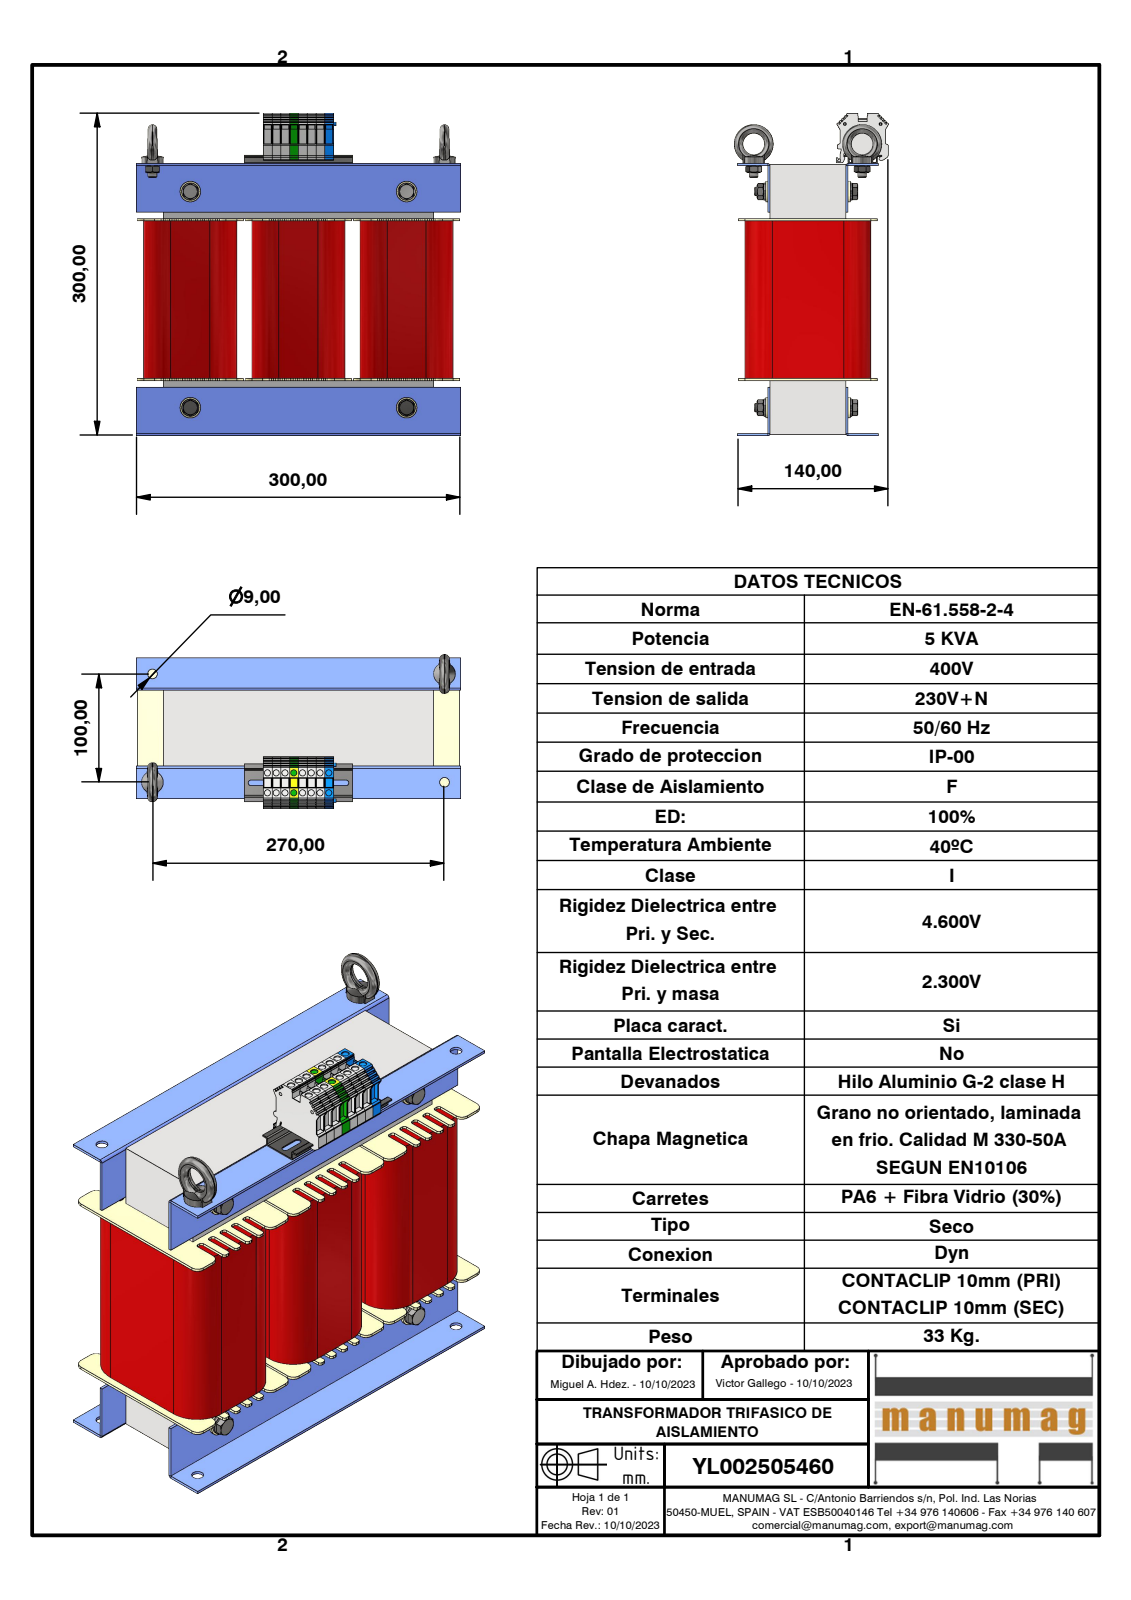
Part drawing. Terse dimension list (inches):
name: YL002505460; 3UI150 250 x 250 - 70 (Rc50); UI 150_70; RC50 NT050 (+8 more)
written by: Autodesk Inventor 2023 (AUTOMOTIVE_DESIGN)
unit: in
bodies: 45 solids, 3220 faces (2108 planar, 936 cylindrical, 176 other)
size: 11.811 × 11.752 × 5.607
volume: 384.8 in³; area: 1 314 in²
holes: 16× ⌀0.224, 6× ⌀0.262, 6× ⌀0.433, 4× ⌀0.315, 4× ⌀0.331, 4× ⌀0.354, 4× ⌀0.413, 2× ⌀0.094, 2× ⌀0.098, 2× ⌀0.108, 2× ⌀0.787
bosses: 4× ⌀0.748, 4× ⌀0.63, 4× ⌀0.449, 4× ⌀0.378, 4× ⌀0.288, 2× ⌀1.417, 2× ⌀0.315, 2× ⌀0.276
rounds: 113× R0.079, 81× R0.012, 24× R0.236, 14× R0.039, 12× R0.984, 8× R0.016, 8× R0.102, 4× R0.02
face distances: 1.969, 3.937, 0.079, 7.874, 2.756, 5.906, 9.843, 0.039, 2.008, 7.835
hole spacings: 0.319, 0.791, 0.638, 0.965, 0.957, 1.2, 0.724, 1.276
